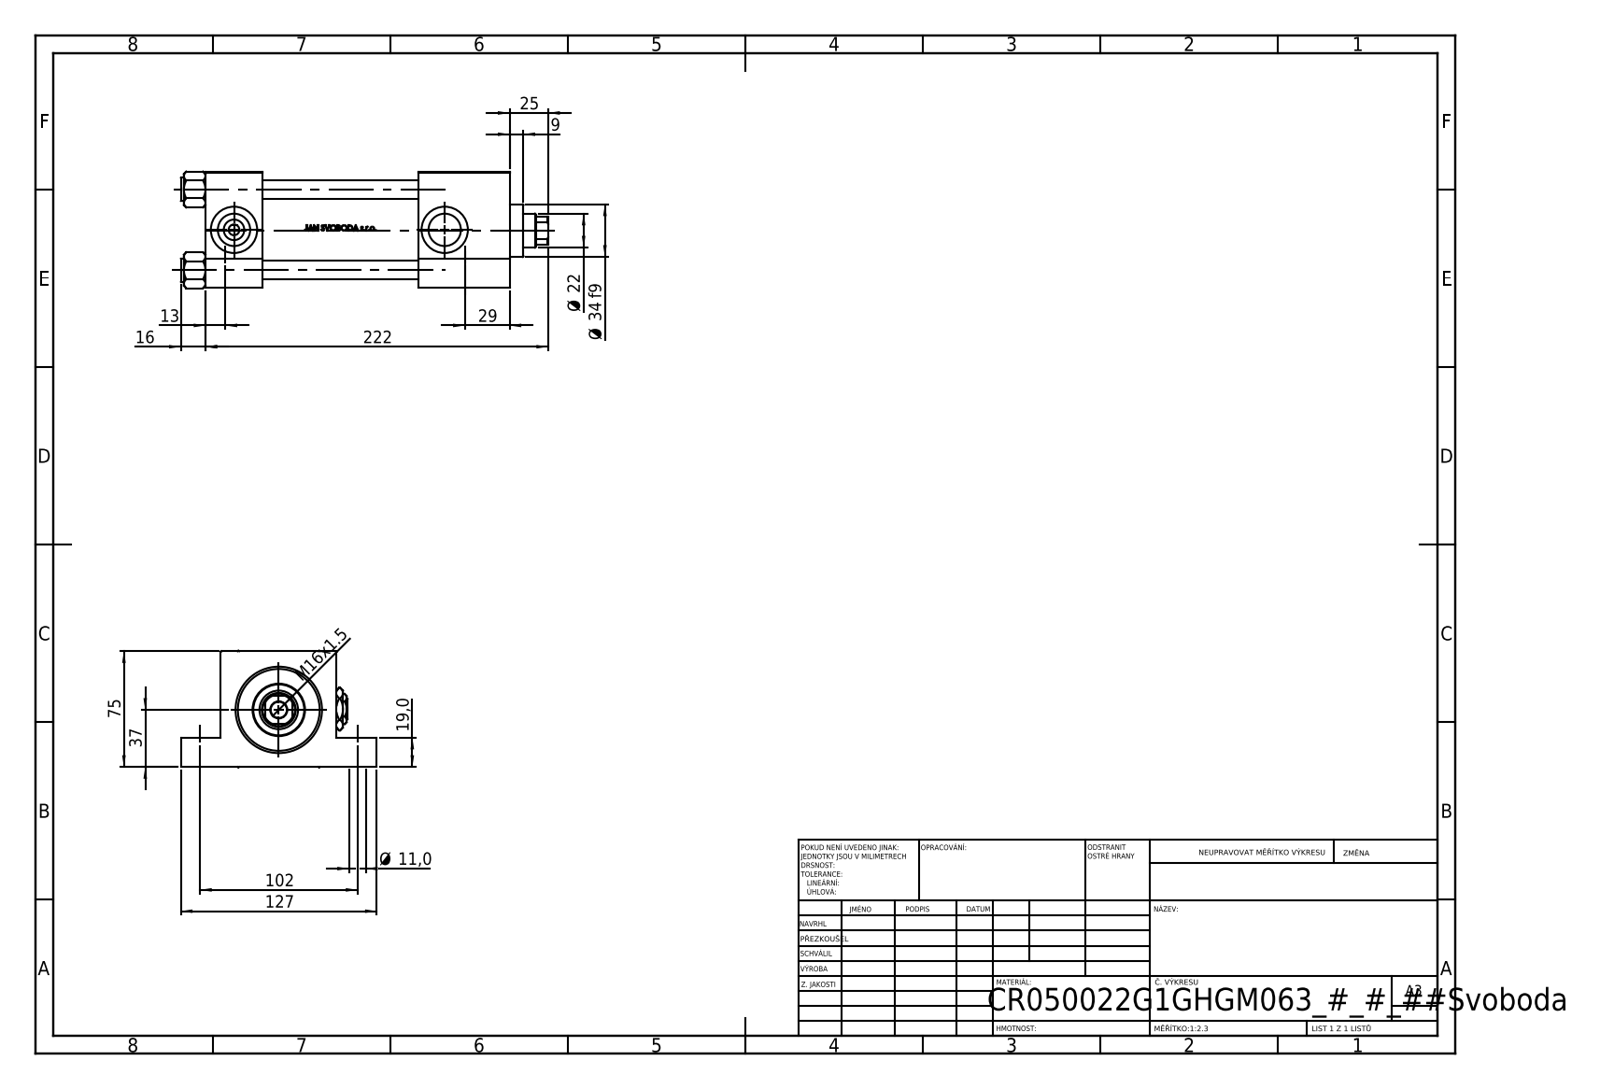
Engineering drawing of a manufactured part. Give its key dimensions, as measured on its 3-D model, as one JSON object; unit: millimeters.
{"part_name": "V215CR_G_Body; V215CR_G_TYCINKA; V215_VC_A; NUT_M5_G (+2 more)", "step_written_by": "SolidWorks 2019 (CONFIG_CONTROL_DESIGN)", "units": "millimeters", "bodies": {"solids": 12, "faces": 1134, "planar": 454, "cylindrical": 128, "other": 552}, "overall_size": [238, 127, 75.54], "volume_mm3": 809681, "surface_area_mm2": 185079, "round_holes": [[11, 4], [12, 4], [7, 2], [20.96, 2], [30, 2], [10.5, 1], [22, 1], [25, 1], [41, 1], [50, 1], [53, 1]], "round_bosses_or_shafts": [[15, 4], [56, 1], [34, 1]], "partial_cylinders_radius": [[10.5, 1]], "face_to_face_distances": [75, 101, 37, 197, 160, 19, 56, 138, 59, 26], "hole_center_spacings": [52.3, 36.63, 37.34, 73.96, 102, 155, 185.55, 136.5]}
